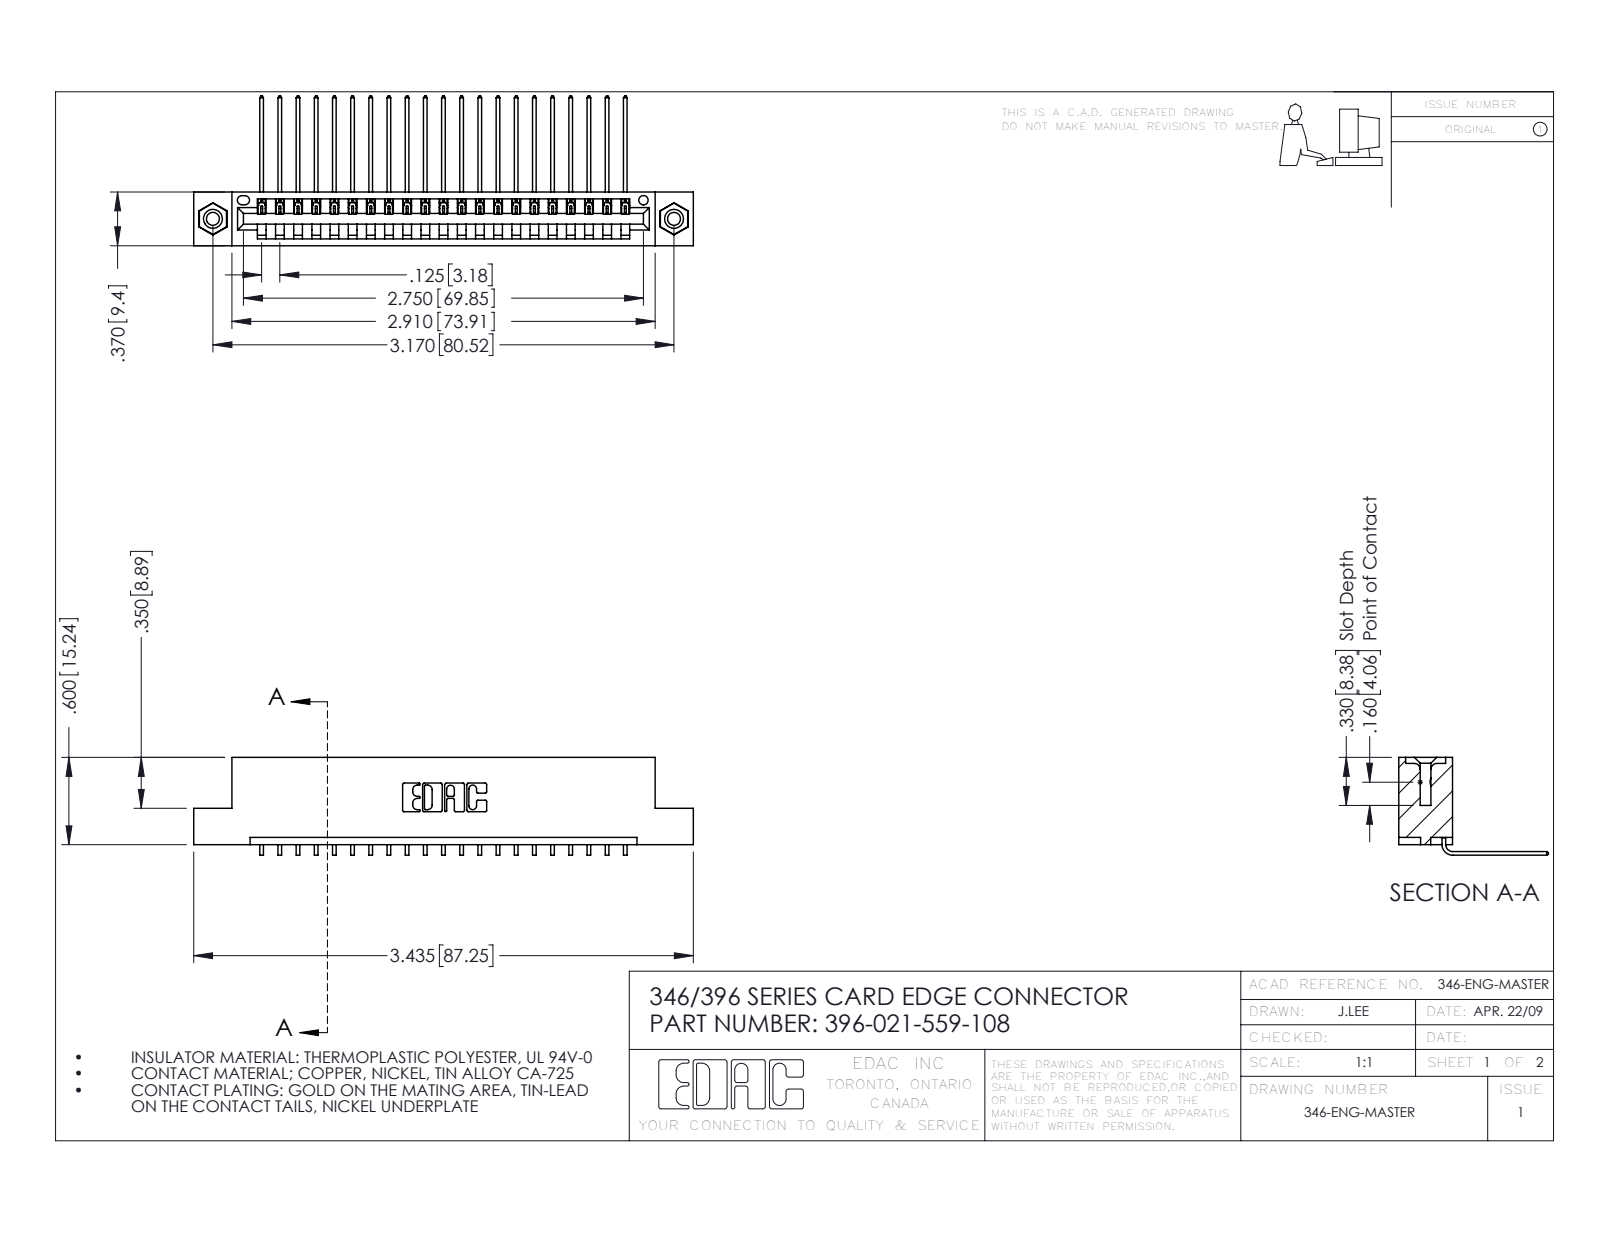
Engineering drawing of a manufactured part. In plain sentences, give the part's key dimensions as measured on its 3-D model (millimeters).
The part is named "346 Part_Flush Mounting Lugs - 0.156 Dia-TI; 396-021-559-108; 345-292-001_558 559 Tail - 1; 345-250-001_345-250-003-102". Its 3-D file was written by "SolidWorks 2016 (CONFIG_CONTROL_DESIGN)". It is 24 solids with 1442 faces: 990 planar, 436 cylindrical and 16 other. Overall it measures 87.2 by 26.2 by 17.1 millimeters. Its volume is 8 280 cubic millimeters and its surface area 10 550 square millimeters. Round holes: 2 of diameter 2.3, 2 of diameter 3.2, 2 of diameter 4, 1 of diameter 1.6. Round bosses or shafts: 2 of diameter 3.9. Partial cylindrical surfaces (rounded edges, fillets, slot ends): 42 of radius 0.2, 22 of radius 0.3, 6 of radius 0.2, 6 of radius 0.8, 3 of radius 0.7, 2 of radius 0.8, 2 of radius 1, 1 of radius 0.4. The main face-to-face distances are 1.2, 8.2, 9.4, 6.4, 1.8, 0.6, 7.6, 3.8, 5.6, 2.5. The hole center spacings are 6.2, 75.3, 80.5.
